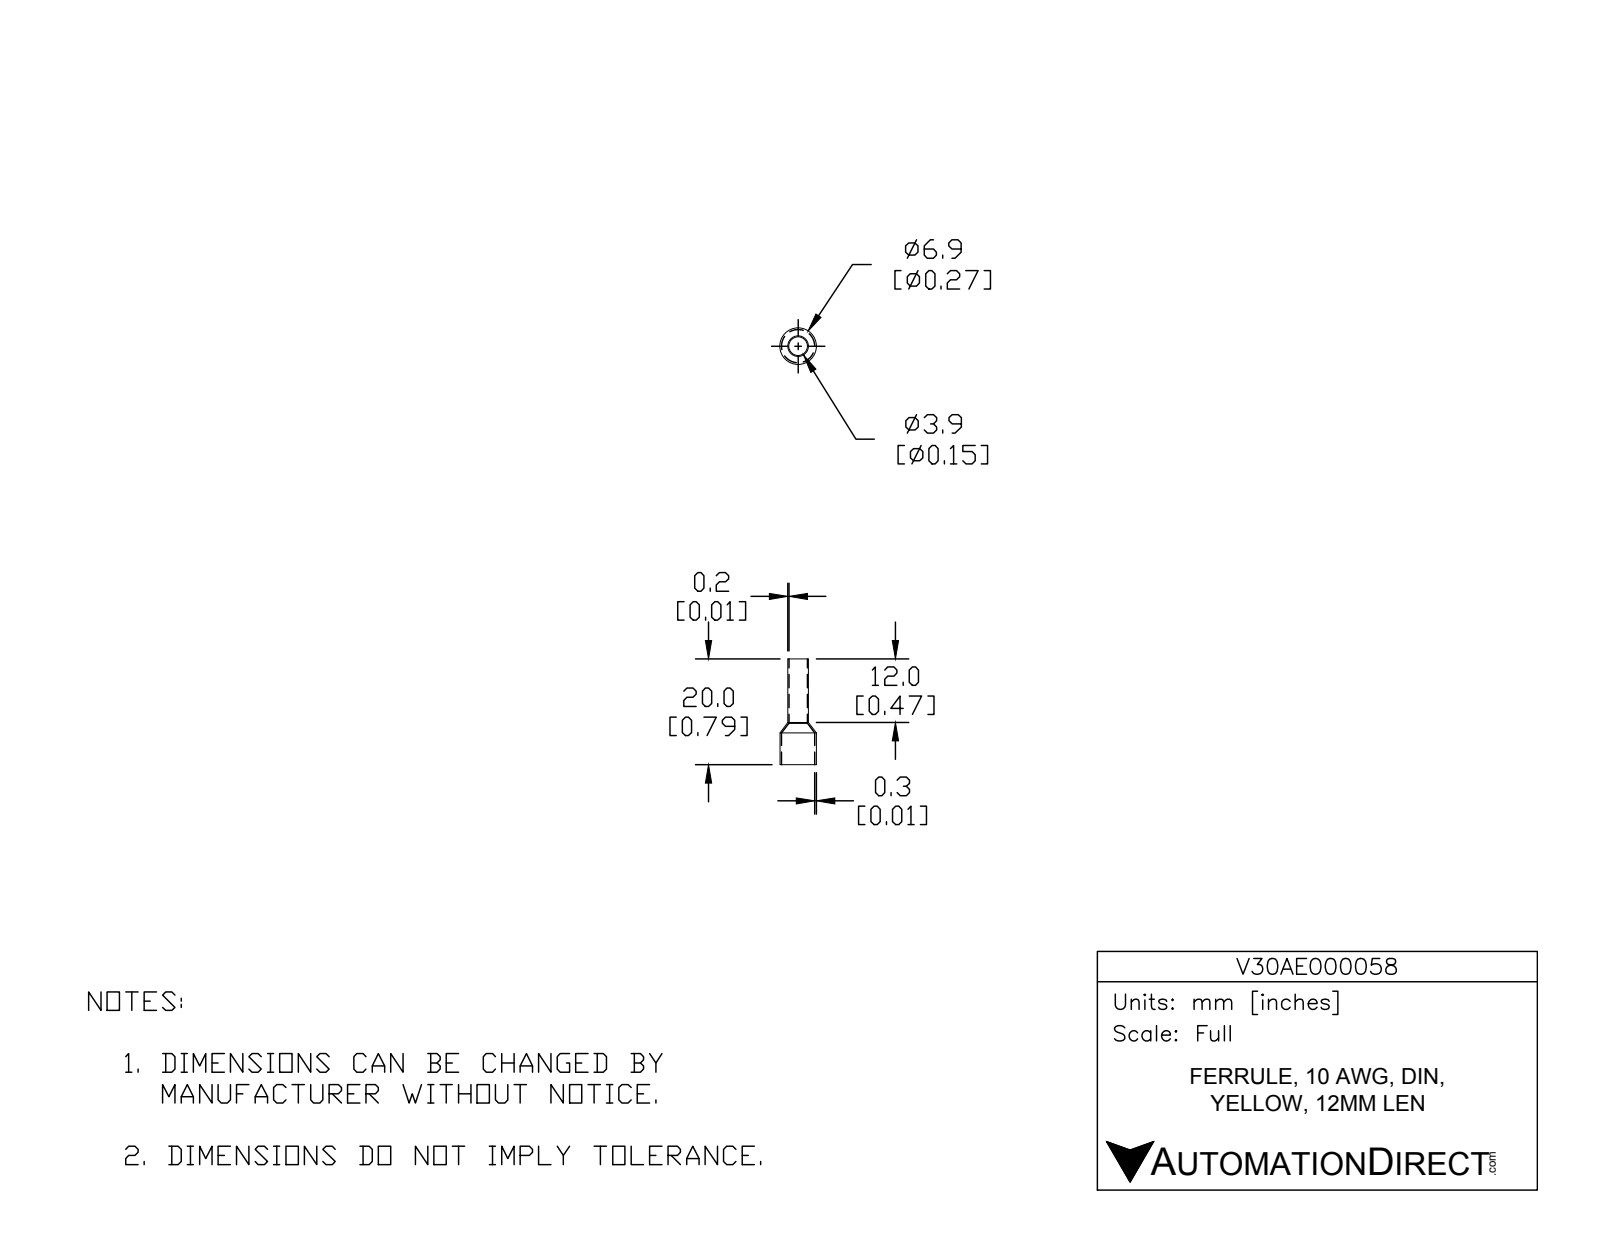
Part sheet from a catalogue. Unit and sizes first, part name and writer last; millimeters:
Units: millimetres
Overall size (bounding box): 20 × 6.9 × 6.9
Round holes (diameter × count): ⌀3.5 ×1, ⌀6.3 ×1
Round bosses / shafts (diameter × count): ⌀6.9 ×1, ⌀3.9 ×1
Main face-to-face distances: 20
Volume: 75 mm³ · Surface area: 616 mm²
Bodies: 1 solid, 14 faces (2 planar, 8 cylindrical, 4 other)
Part name (STEP PRODUCT): V30AE000058
STEP written by: SolidWorks 2017 (AUTOMOTIVE_DESIGN)
